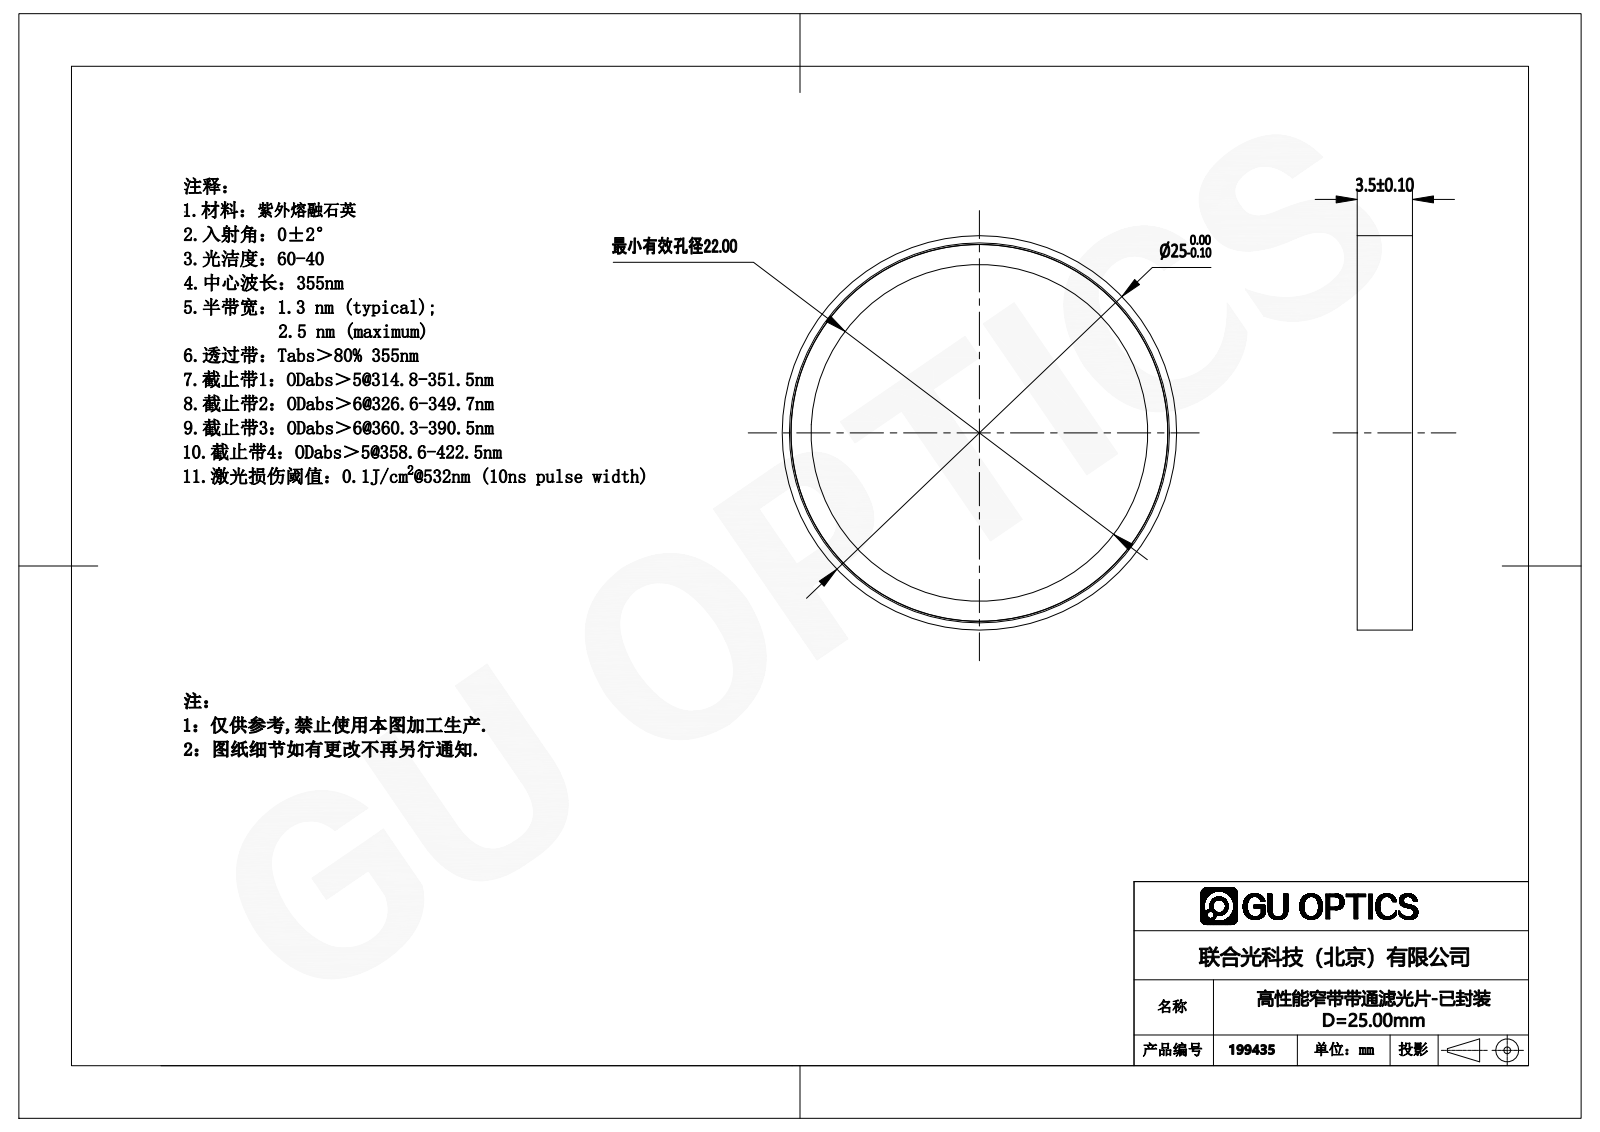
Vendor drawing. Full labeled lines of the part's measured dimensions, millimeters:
Part name (STEP PRODUCT): 199435
STEP written by: SolidWorks 2019 (CONFIG_CONTROL_DESIGN)
Units: millimetres
Bodies: 3 solids, 22 faces (8 planar, 14 cylindrical, 0 other)
Overall size (bounding box): 24.99 × 24.99 × 3.5
Volume: 1 092 mm³ · Surface area: 2 102 mm²
Round holes (diameter × count): ⌀21.21 ×1, ⌀21.34 ×1, ⌀24.08 ×1, ⌀24.21 ×1
Round bosses / shafts (diameter × count): ⌀24.99 ×1, ⌀23.9 ×1, ⌀23.88 ×1
Main face-to-face distances: 2, 0.38, 2.38, 2.76, 3.5, 3.12, 1.12, 0.74, 0.69, 0.31
